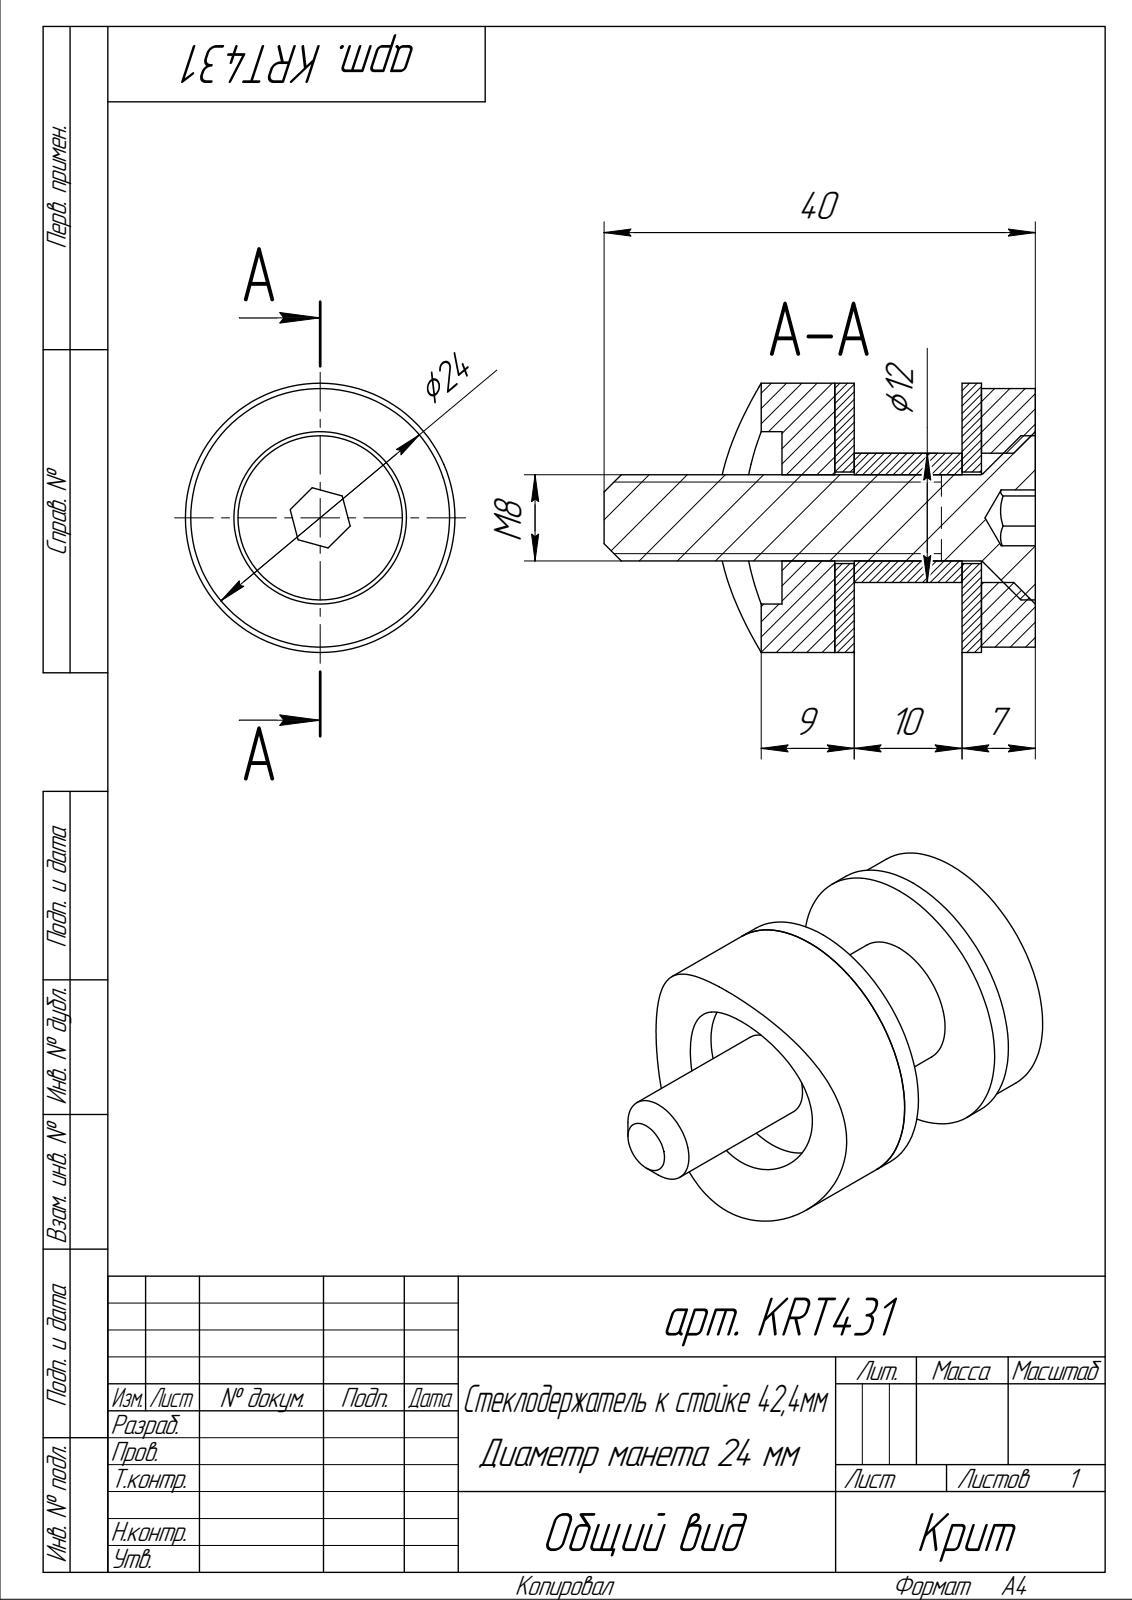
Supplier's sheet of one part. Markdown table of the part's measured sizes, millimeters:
| quantity | value |
| --- | --- |
| part name | Сборка; Деталь; Hexagon socket countersunk head screw ISO 10642 - Ì8 x 40 - 10.9 |
| STEP written by | ASCON Math Kernel (AUTOMOTIVE_DESIGN) |
| units | millimeters |
| bodies | 6 solids, 38 faces (18 planar, 14 cylindrical, 6 other) |
| overall size | 40 × 25 × 25 |
| volume | 9 212 mm³ |
| surface area | 7 322 mm² |
| round holes (diameter × count) | 8 × 1, 8.5 × 1, 12 × 1, 16 × 1 |
| round bosses / shafts (diameter × count) | 25 × 1, 24 × 1, 15.24 × 1 |
| partial cylindrical surfaces (radius × count) | 21.2 × 1 |
| main face-to-face distances | 1.8, 11.8, 13.6, 10, 5, 6.8, 16.8, 18.6, 23.5, 18.5 |
